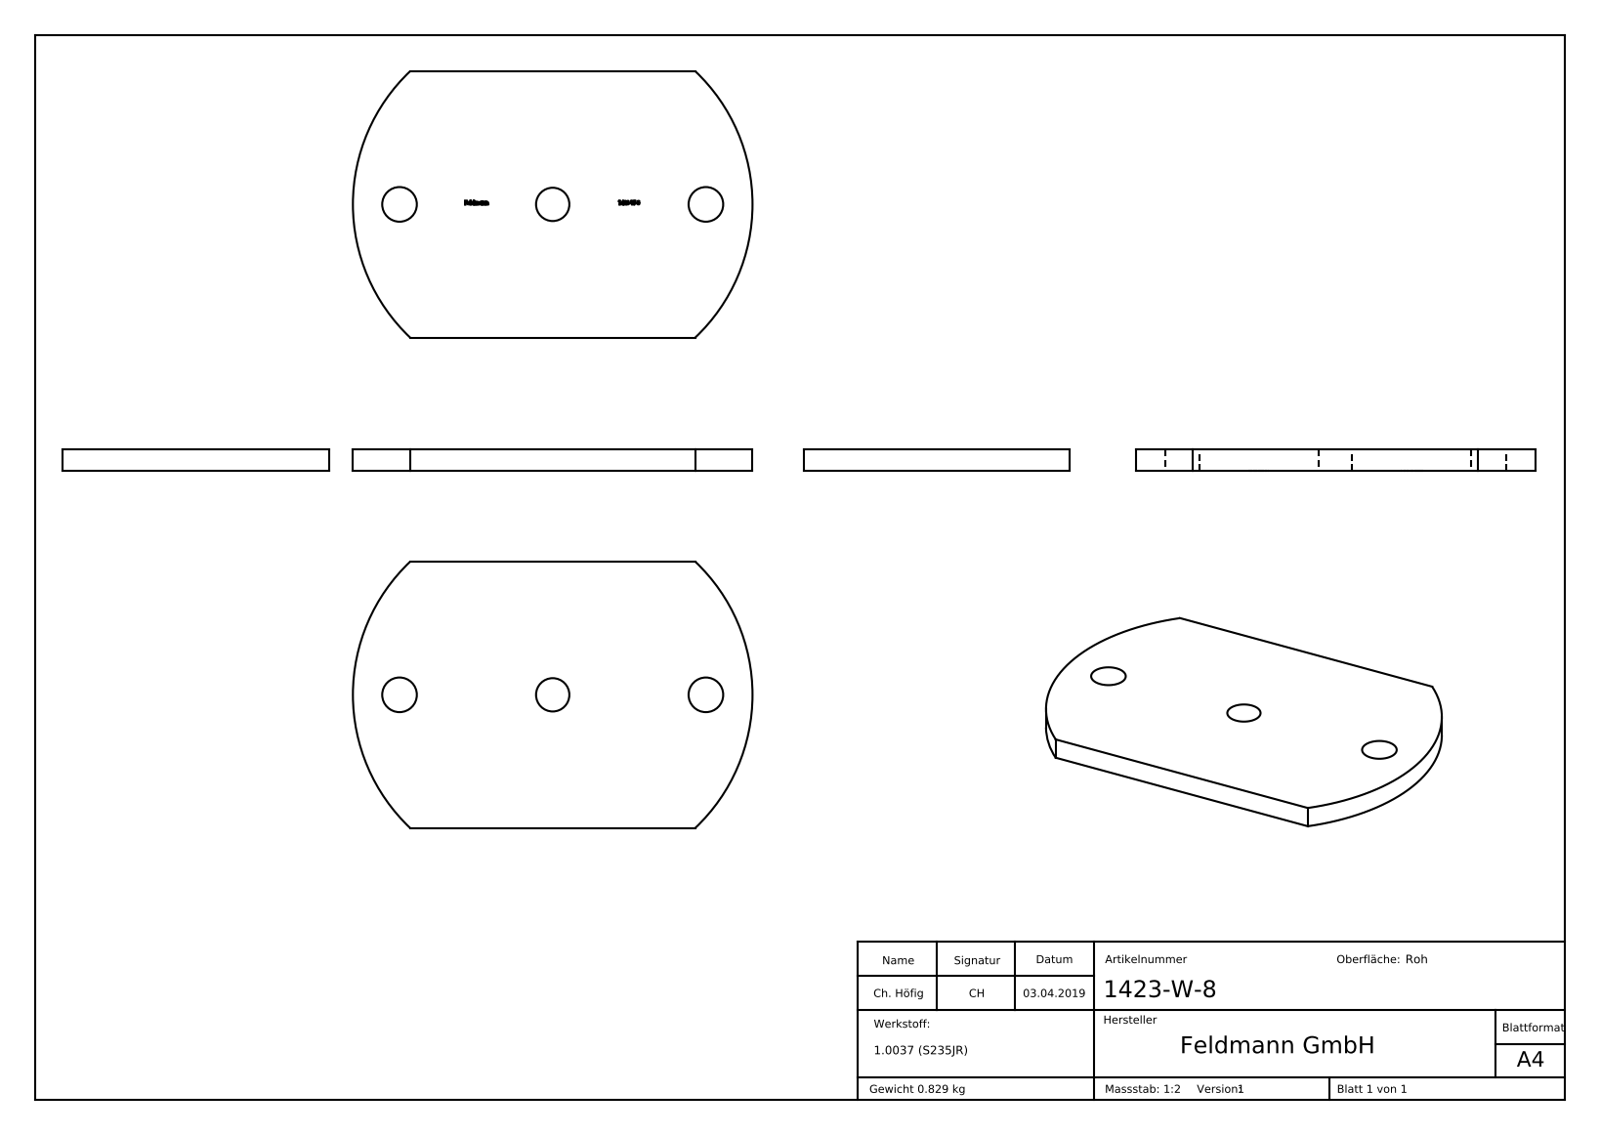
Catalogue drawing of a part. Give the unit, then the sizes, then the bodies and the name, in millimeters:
Units: millimetres
Overall size (bounding box): 150 × 100 × 8
Round holes (diameter × count): ⌀13 ×2, ⌀12.5 ×1
Partial cylindrical surfaces — rounded edges, fillets, slot ends (radius × count): R68.89 ×2
Main face-to-face distances: 8, 100, 7.9, 0.54, 55.98, 2.03, 1.12, 58.01, 1.24, 54.74
Hole centre spacings: 57.5, 115
Volume: 106 254 mm³ · Surface area: 31 043 mm²
Bodies: 1 solid, 222 faces (129 planar, 8 cylindrical, 85 other)
Part name (STEP PRODUCT): 1423-W-8
STEP written by: SolidWorks 2015 (CONFIG_CONTROL_DESIGN)
